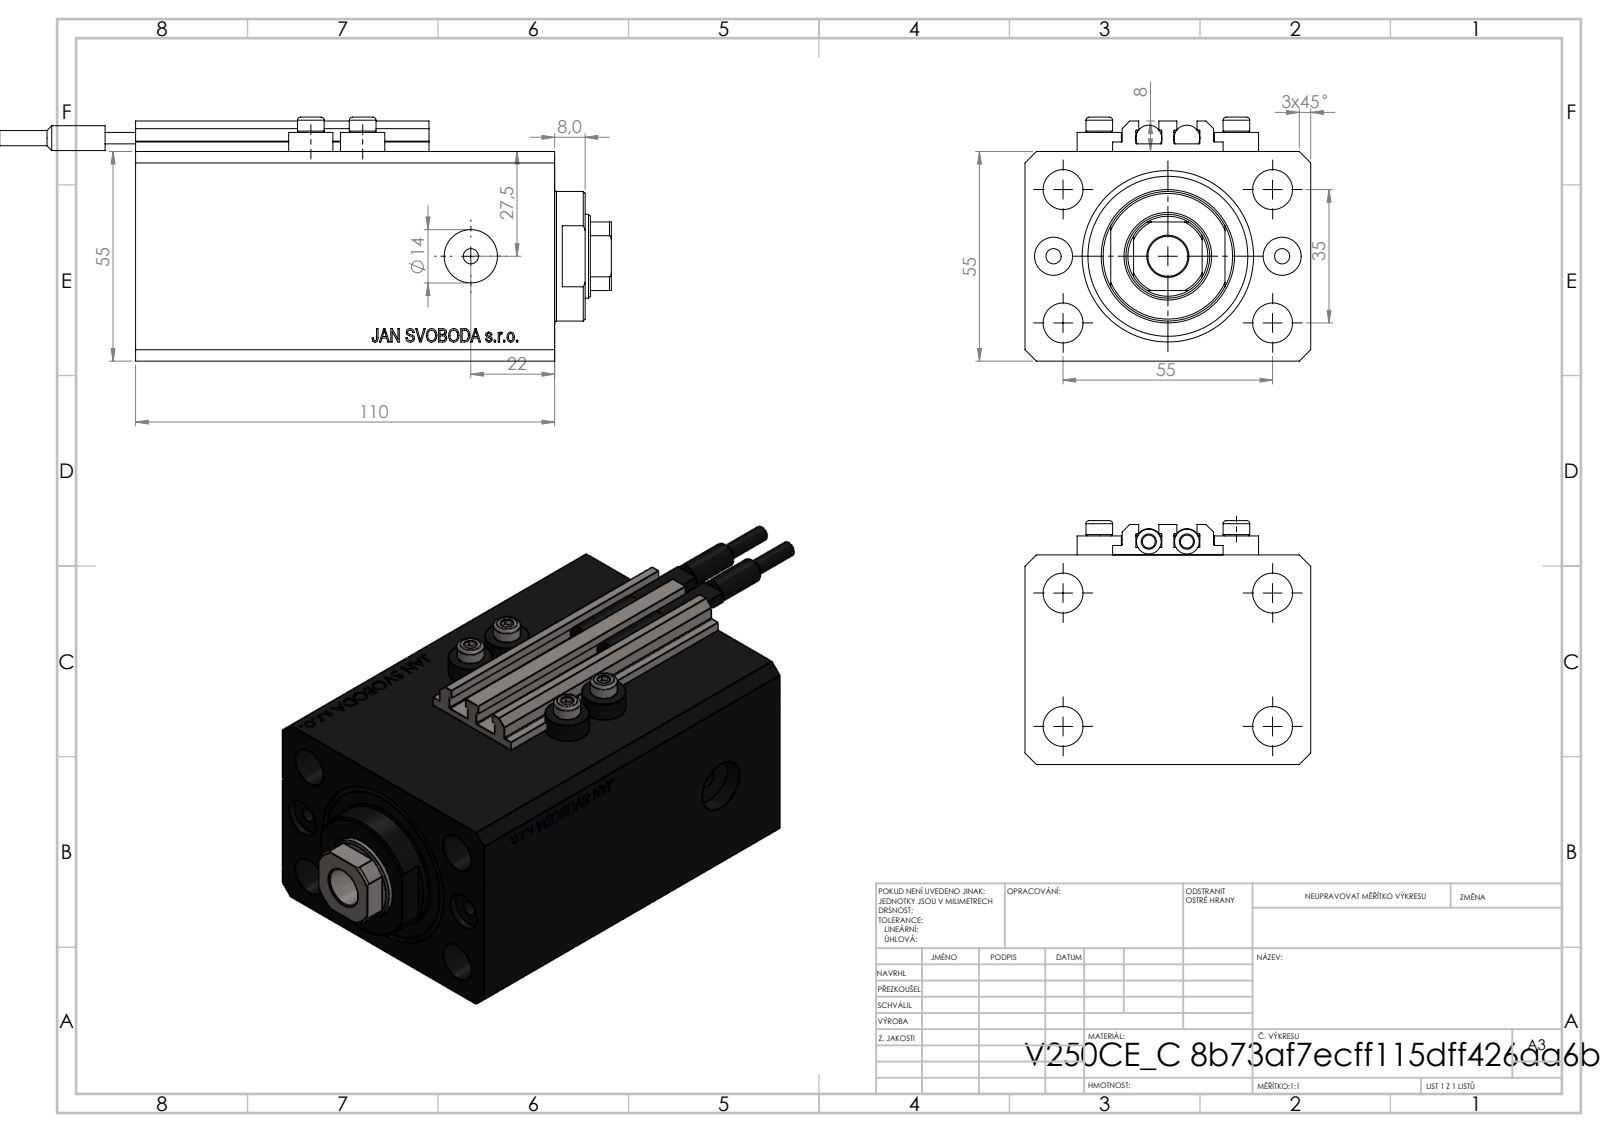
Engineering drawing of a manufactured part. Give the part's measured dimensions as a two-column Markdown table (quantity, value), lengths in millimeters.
| quantity | value |
| --- | --- |
| part name | V250CE_C_VCP; V250CE_VC_C; V250CE_C_Body; ALLEN BOLT V250CE (+1 more) |
| STEP written by | SolidWorks 2019 (CONFIG_CONTROL_DESIGN) |
| units | millimeters |
| bodies | 10 solids, 1085 faces (535 planar, 98 cylindrical, 452 other) |
| overall size | 160.9 × 75 × 64 |
| volume | 412 441 mm³ |
| surface area | 96 523 mm² |
| round holes (diameter × count) | 4 × 8, 10.5 × 5, 10 × 2, 14 × 2, 22 × 1, 32 × 1, 45 × 1 |
| round bosses / shafts (diameter × count) | 11.6 × 4, 7 × 4, 6.8 × 2, 6.5 × 2, 4 × 2, 34 × 1 |
| partial cylindrical surfaces (radius × count) | 0.2 × 10, 10.5 × 1 |
| main face-to-face distances | 55, 75, 110, 82.9, 27.1, 3, 9.9, 73, 100.1, 2 |
| hole center spacings | 17.68, 32.6, 60.1, 13.6, 30, 35, 36, 38.48 |
